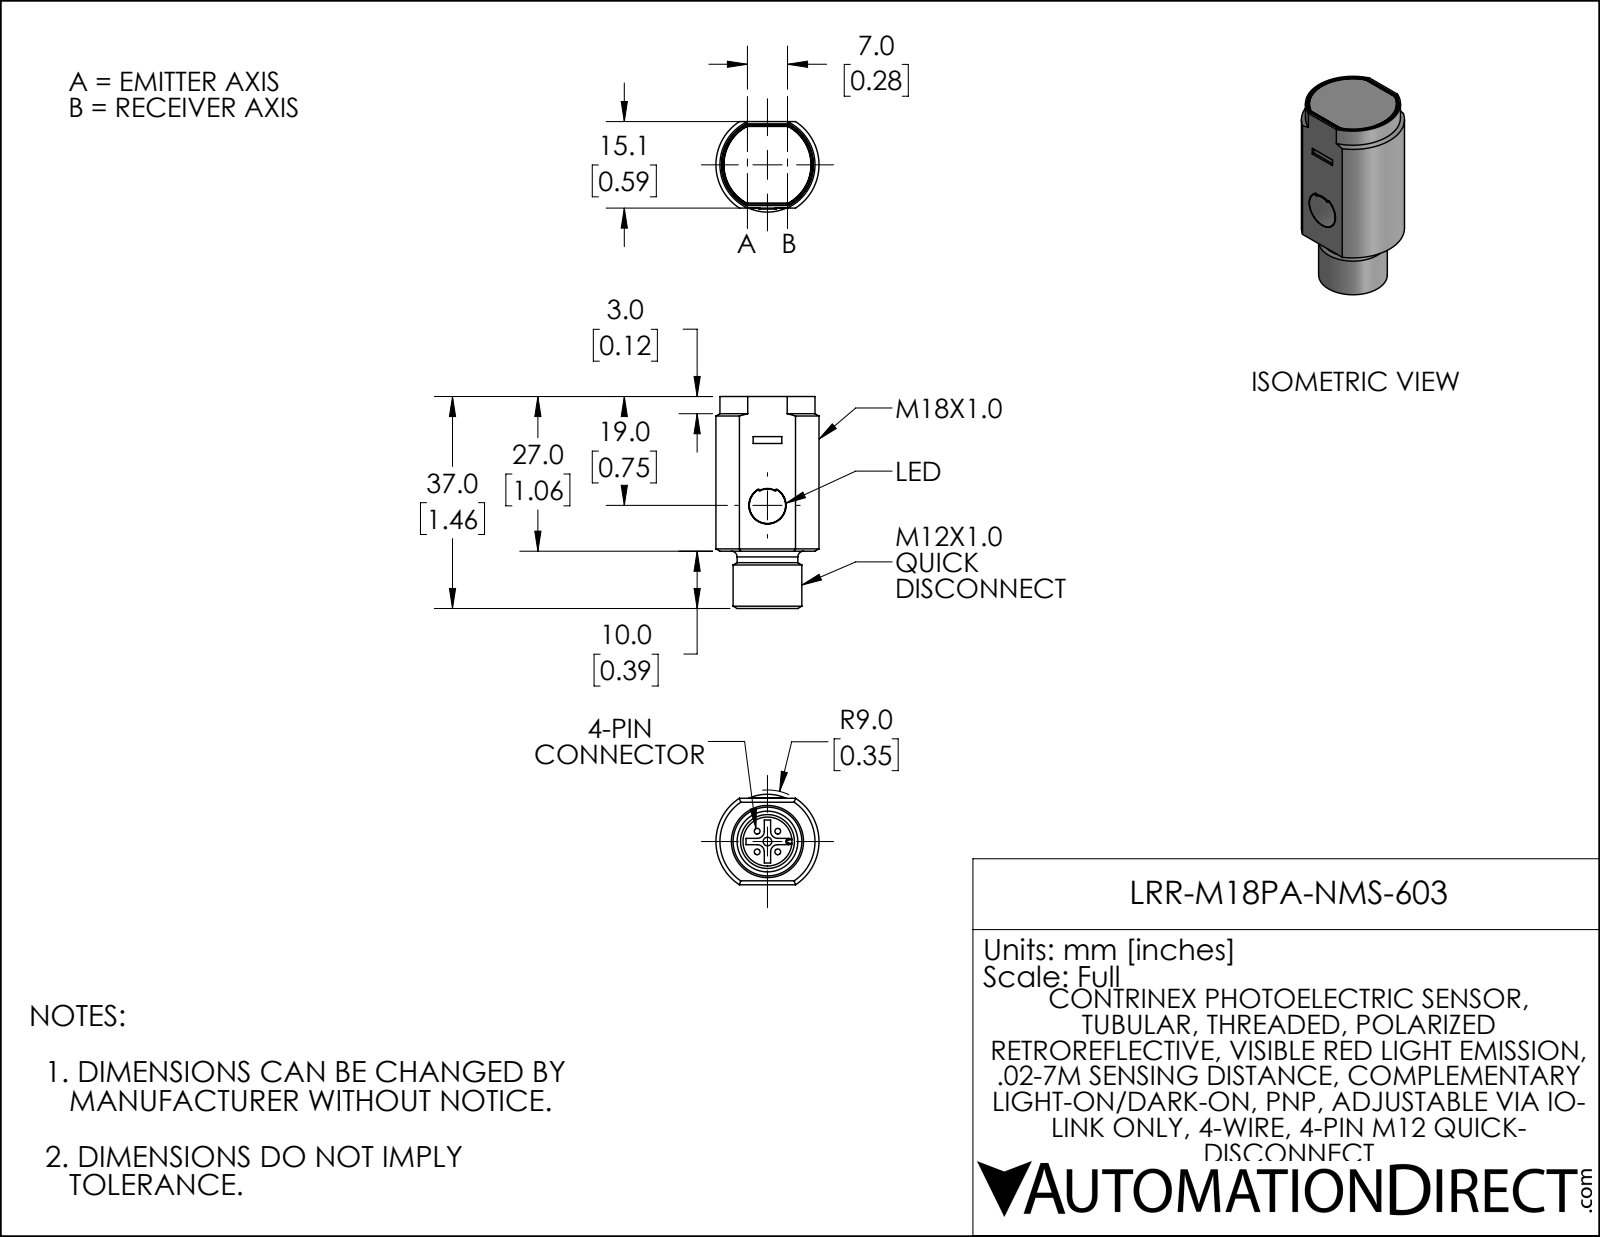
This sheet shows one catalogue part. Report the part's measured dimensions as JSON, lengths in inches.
{"part_name": "LRR-M18PA-NMS-603", "step_written_by": "SolidWorks 2021 (AUTOMOTIVE_DESIGN)", "units": "inches", "bodies": {"solids": 1, "faces": 125, "planar": 56, "cylindrical": 54, "other": 15}, "overall_size": [1.457, 0.709, 0.622], "volume_in3": 0.418, "surface_area_in2": 4.241, "round_holes": [[0.059, 1], [0.256, 1], [0.336, 1]], "round_bosses_or_shafts": [[0.039, 4], [0.472, 1], [0.417, 1]], "partial_cylinders_radius": [[0.006, 8], [0.014, 8], [0.028, 8], [0.049, 4], [0.008, 2], [0.02, 1], [0.112, 1], [0.116, 1]], "face_to_face_distances": [0.594, 1.061, 0.047, 1.108, 1.063, 1.11, 0.016, 1.457, 1.455, 0.394]}
